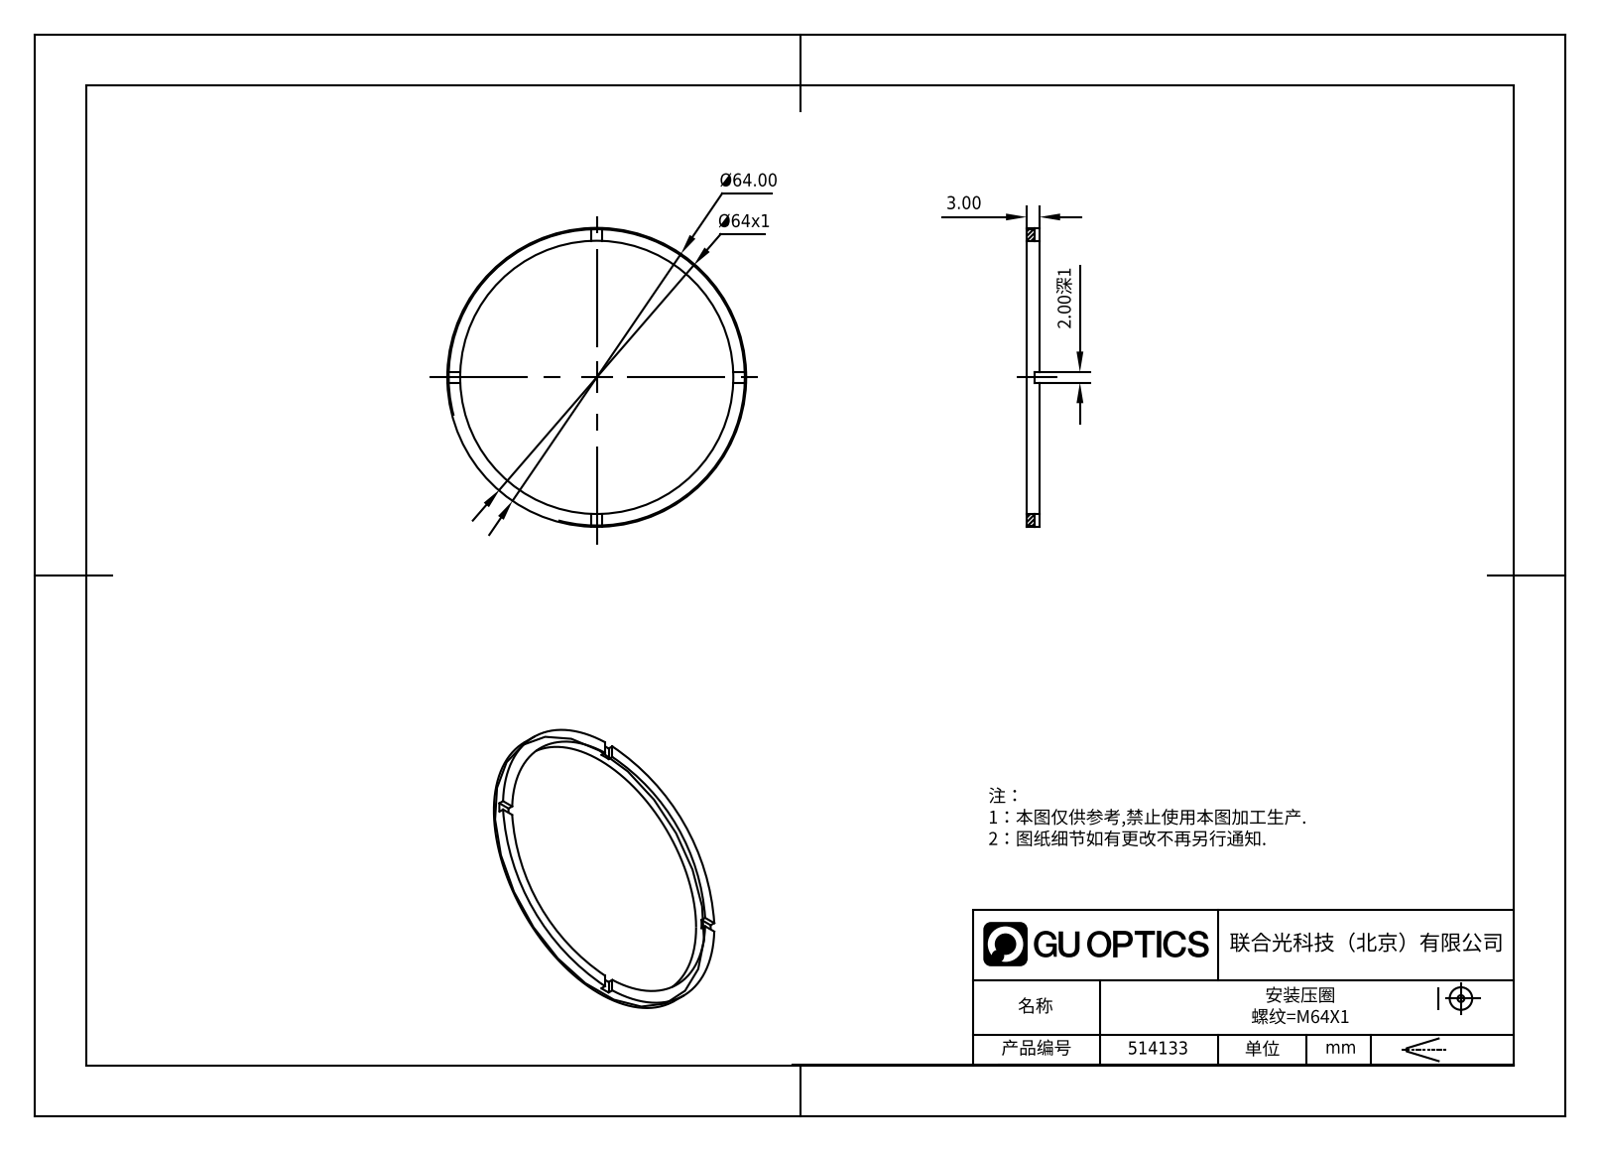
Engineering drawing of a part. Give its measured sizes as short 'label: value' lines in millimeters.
name: 514133
written by: SolidWorks 2020 (CONFIG_CONTROL_DESIGN)
unit: mm
bodies: 1 solid, 21 faces (17 planar, 4 cylindrical, 0 other)
size: 64 × 64 × 3
volume: 1 429 mm³; area: 2 129 mm²
holes: 1× ⌀59
bosses: 1× ⌀64
face distances: 3, 2, 1
